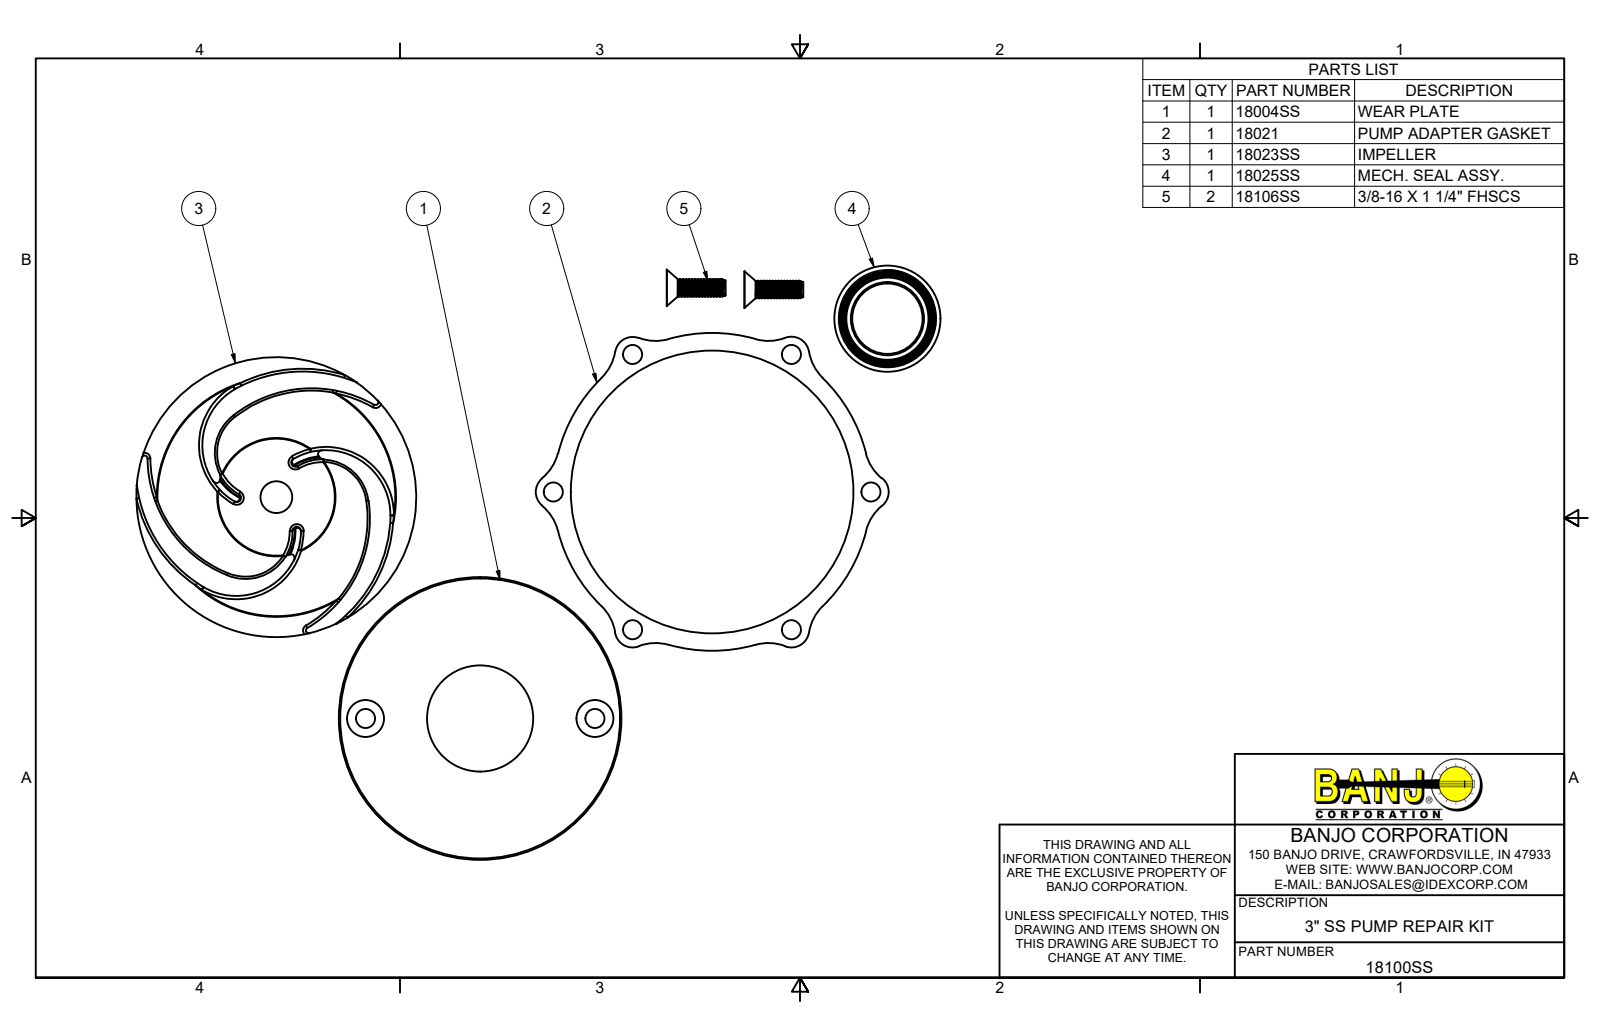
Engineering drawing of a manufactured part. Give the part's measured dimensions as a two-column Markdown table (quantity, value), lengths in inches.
| quantity | value |
| --- | --- |
| part name | 18100SS; 18004SS; 18021; 18023SS (+3 more) |
| STEP written by | Autodesk Inventor 2019 (AUTOMOTIVE_DESIGN) |
| units | inches |
| bodies | 6 solids, 554 faces (116 planar, 151 cylindrical, 287 other) |
| overall size | 17.089 × 12.615 × 4.779 |
| volume | 22.82 in³ |
| surface area | 215.9 in² |
| round holes (diameter × count) | 0.406 × 8, 0.25 × 3, 1.002 × 1, 1.022 × 1, 1.5 × 1, 1.55 × 1, 1.613 × 1, 1.625 × 1, 2.25 × 1, 6.01 × 1 |
| round bosses / shafts (diameter × count) | 0.324 × 30, 0.375 × 2, 6 × 1, 5.95 × 1, 2.5 × 1, 2.125 × 1, 2.063 × 1, 2 × 1 |
| partial cylindrical surfaces (radius × count) | 1 × 15, 0.06 × 6, 0.375 × 6, 0.162 × 4, 0.089 × 3, 1.375 × 3, 2.688 × 3, 2.969 × 3 |
| main face-to-face distances | 0.25, 3.531, 3.281, 0.031, 0.281, 3.25, 0.75, 3.781, 1, 3.5 |
| hole center spacings | 3.375, 5.846, 3.375, 2.775, 6.75, 1.017, 2.437, 2 |
